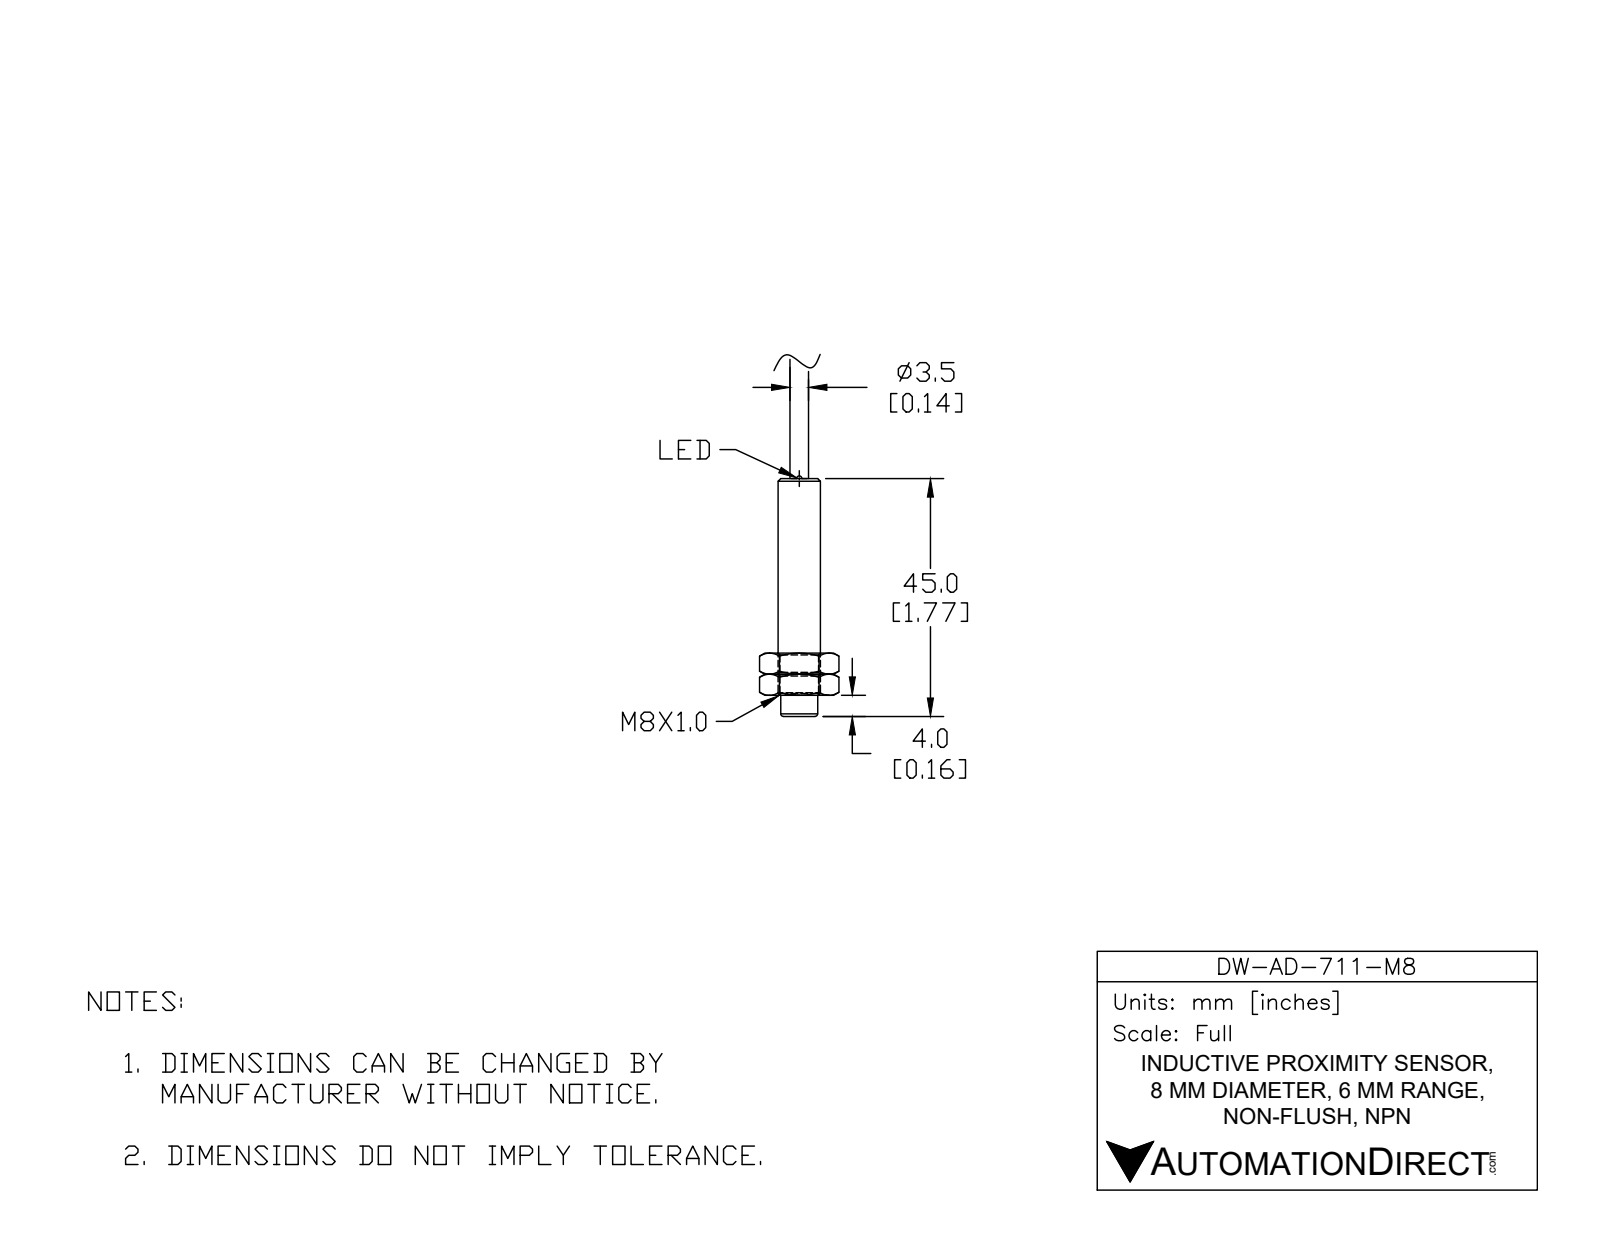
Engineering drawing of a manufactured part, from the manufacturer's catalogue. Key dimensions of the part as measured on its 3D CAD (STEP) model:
Part name (STEP PRODUCT): DW-AD-711-M8
STEP written by: SolidWorks 2017 (AUTOMOTIVE_DESIGN)
Units: inches
Bodies: 2 solids, 9 faces (4 planar, 3 cylindrical, 2 other)
Overall size (bounding box): 2.559 × 0.315 × 0.315
Volume: 0.147 in³ · Surface area: 2.236 in²
Round bosses / shafts (diameter × count): ⌀0.315 ×1, ⌀0.276 ×1, ⌀0.138 ×1
Main face-to-face distances: 1.772, 0.787, 2.559
